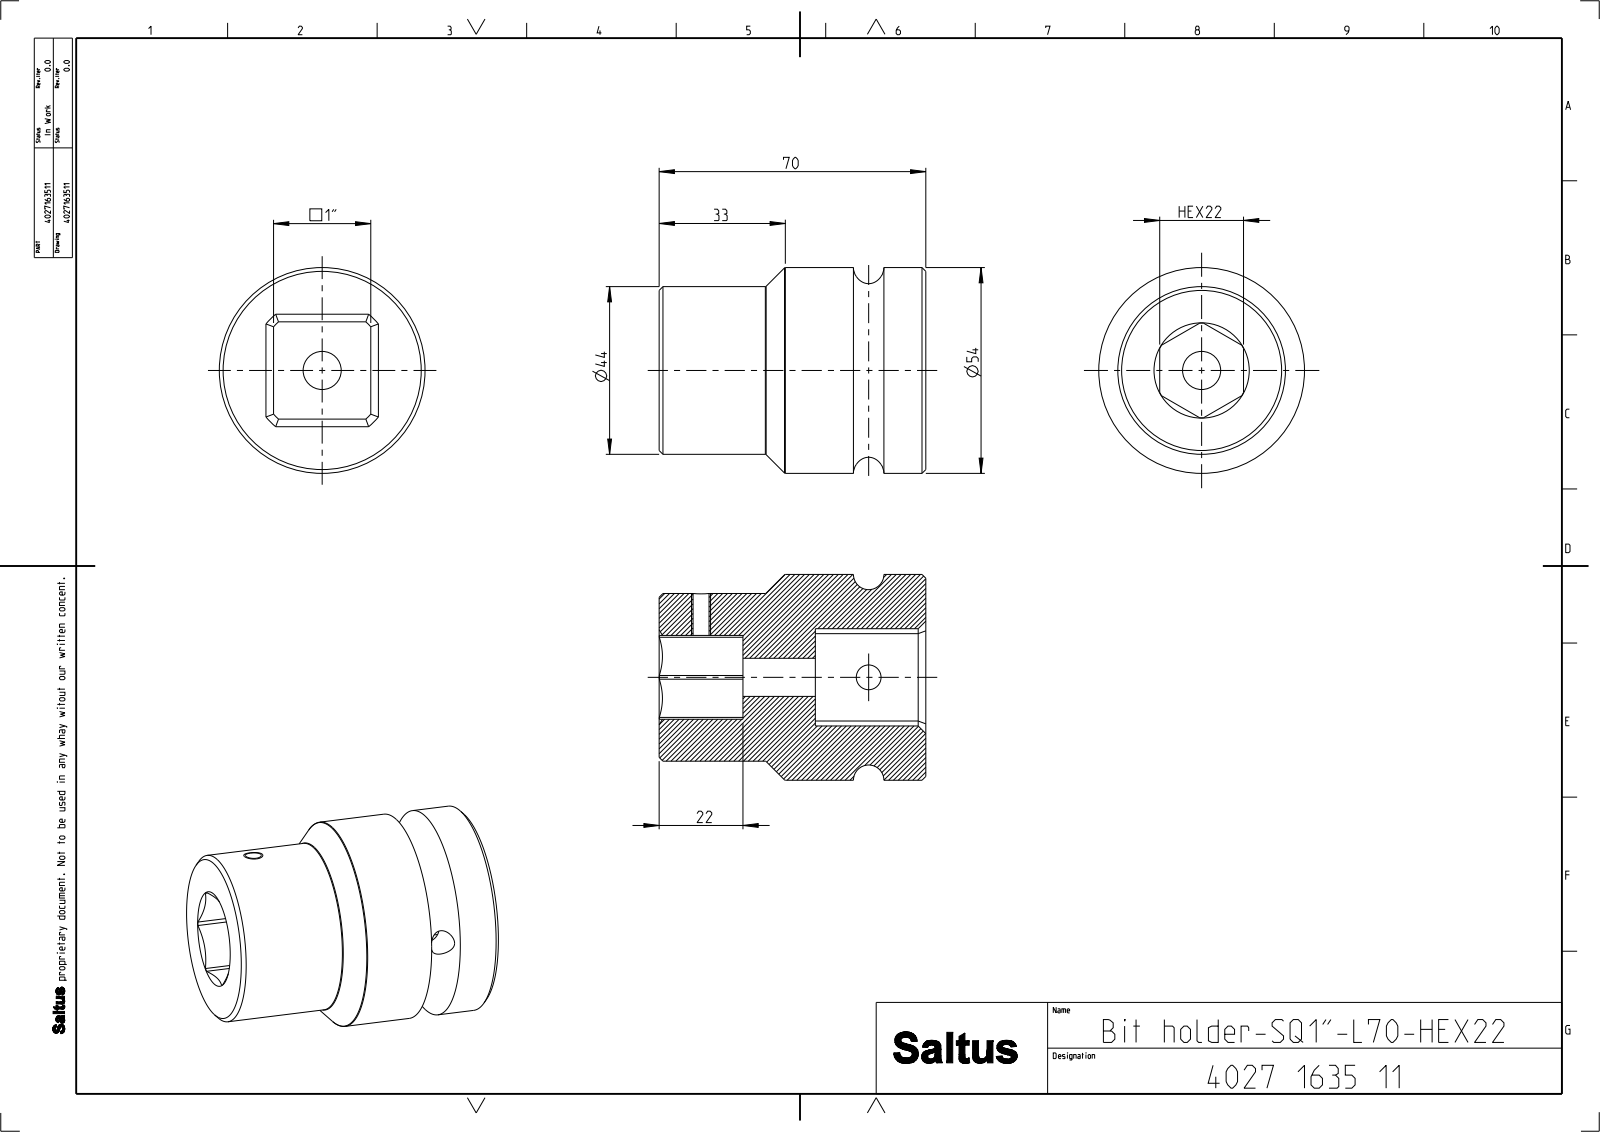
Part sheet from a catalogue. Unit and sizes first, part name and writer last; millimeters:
Units: millimetres
Overall size (bounding box): 70 × 54 × 54
Round holes (diameter × count): ⌀4.2 ×1, ⌀5 ×1, ⌀6.5 ×1, ⌀10 ×1
Round bosses / shafts (diameter × count): ⌀54 ×1, ⌀44 ×1
Partial cylindrical surfaces — rounded edges, fillets, slot ends (radius × count): R12.43 ×1, R17.15 ×1
Main face-to-face distances: 25.52, 22, 70, 29, 41, 1.76, 23.76, 48, 19
Volume: 102 055 mm³ · Surface area: 20 855 mm²
Bodies: 1 solid, 62 faces (18 planar, 26 cylindrical, 18 other)
Part name (STEP PRODUCT): 4027163511
STEP written by: CREO PARAMETRIC BY PTC INC, 2022414 (CONFIG_CONTROL_DESIGN)
